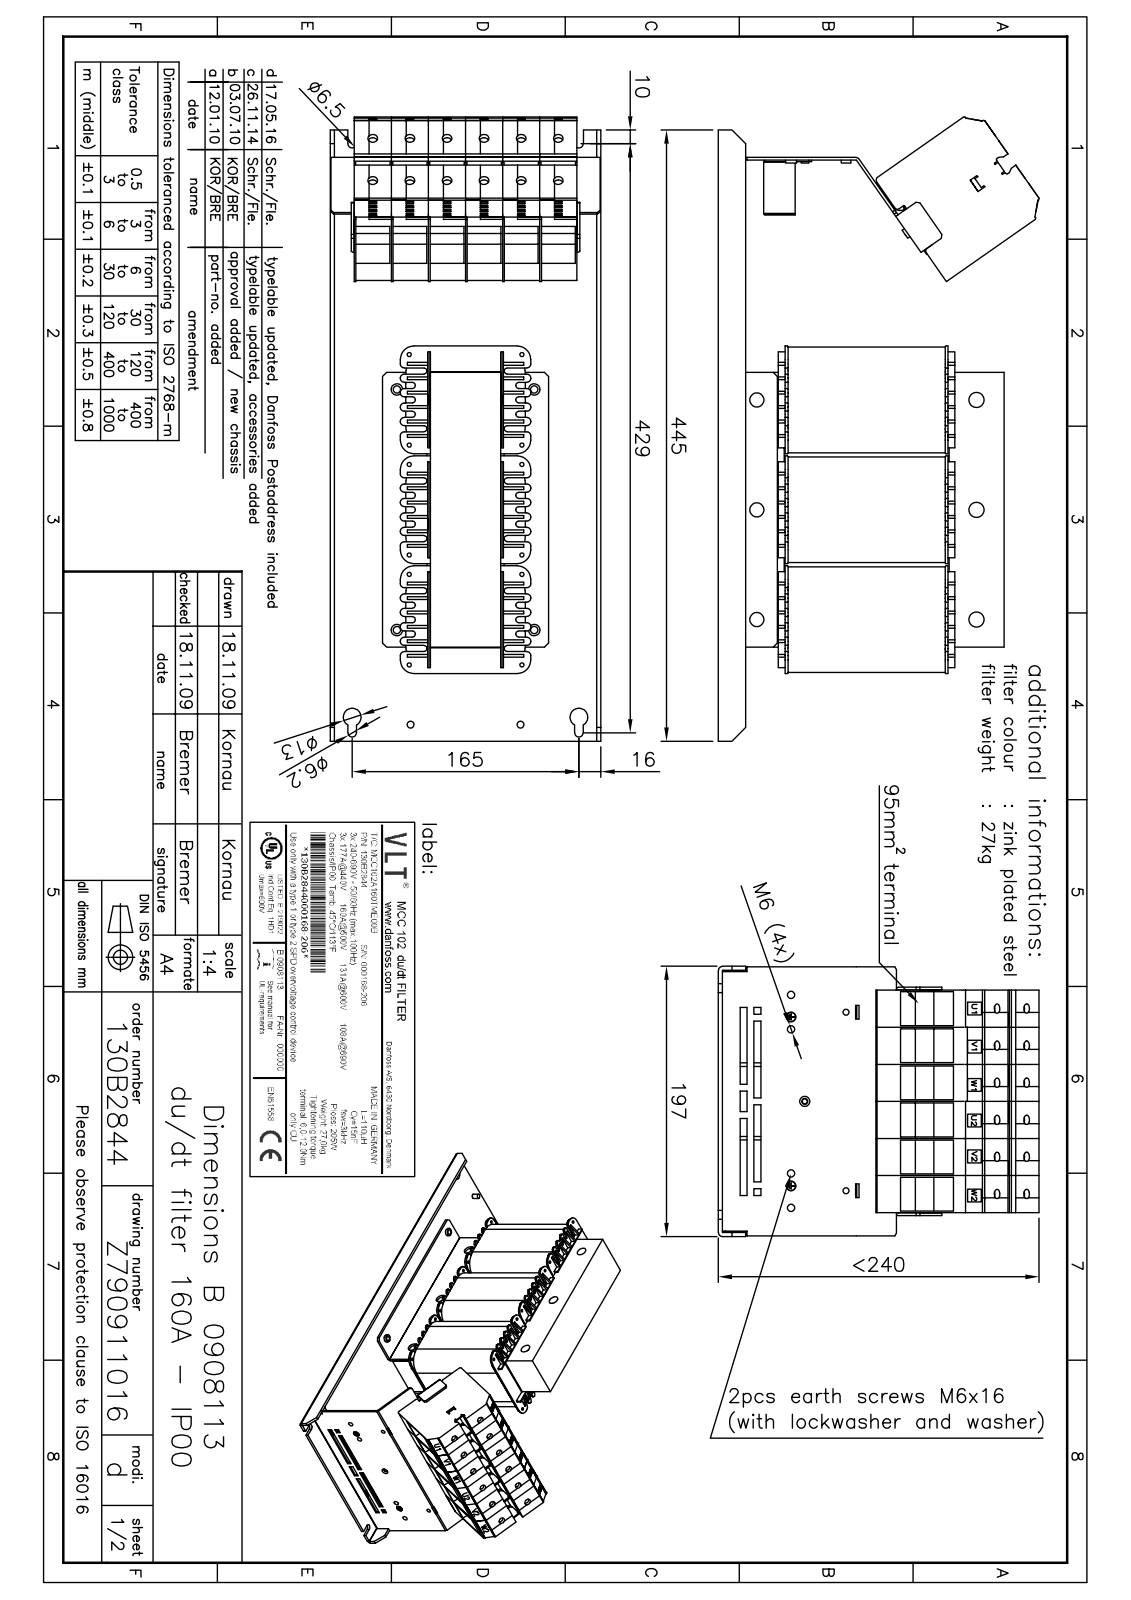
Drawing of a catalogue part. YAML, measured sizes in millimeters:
part_name: "#020-1796; countersunk flat head cross recess screw_din_ISO 7046-1 - M4 x 8 - Z --- 8N; 130B2844; #060-0426 (+8 more)"
step_written_by: "SolidWorks 2014 (AUTOMOTIVE_DESIGN)"
units: millimeters
bodies: {solids: 100, faces: 4853, planar: 3151, cylindrical: 1052, other: 650}
overall_size: [521.85, 236.33, 197]
volume: 4705000
surface_area: 1382000
round_holes:
  - {diameter: 6, count: 19}
  - {diameter: 3, count: 12}
  - {diameter: 5, count: 12}
  - {diameter: 7, count: 12}
  - {diameter: 6.4, count: 10}
  - {diameter: 5.5, count: 6}
  - {diameter: 8.5, count: 6}
  - {diameter: 10, count: 6}
  - {diameter: 3.7, count: 4}
  - {diameter: 6.1, count: 4}
  - {diameter: 7.15, count: 4}
  - {diameter: 13, count: 4}
round_bosses_or_shafts:
  - {diameter: 8, count: 12}
  - {diameter: 12, count: 10}
  - {diameter: 18, count: 6}
  - {diameter: 11.3, count: 6}
  - {diameter: 11.8, count: 4}
  - {diameter: 10, count: 4}
  - {diameter: 7, count: 4}
  - {diameter: 6.95, count: 4}
partial_cylinders:
  - {radius: 0.5, count: 86}
  - {radius: 2.2, count: 60}
  - {radius: 2.9, count: 60}
  - {radius: 0.2, count: 32}
  - {radius: 0.1, count: 18}
  - {radius: 10, count: 14}
  - {radius: 20, count: 12}
  - {radius: 1, count: 8}
face_to_face_distances: [2, 3, 40, 1, 80, 1.5, 81, 53, 0.5, 27]
hole_center_spacings: [80, 27, 46.21, 54, 65.75, 114.56, 160, 100]
